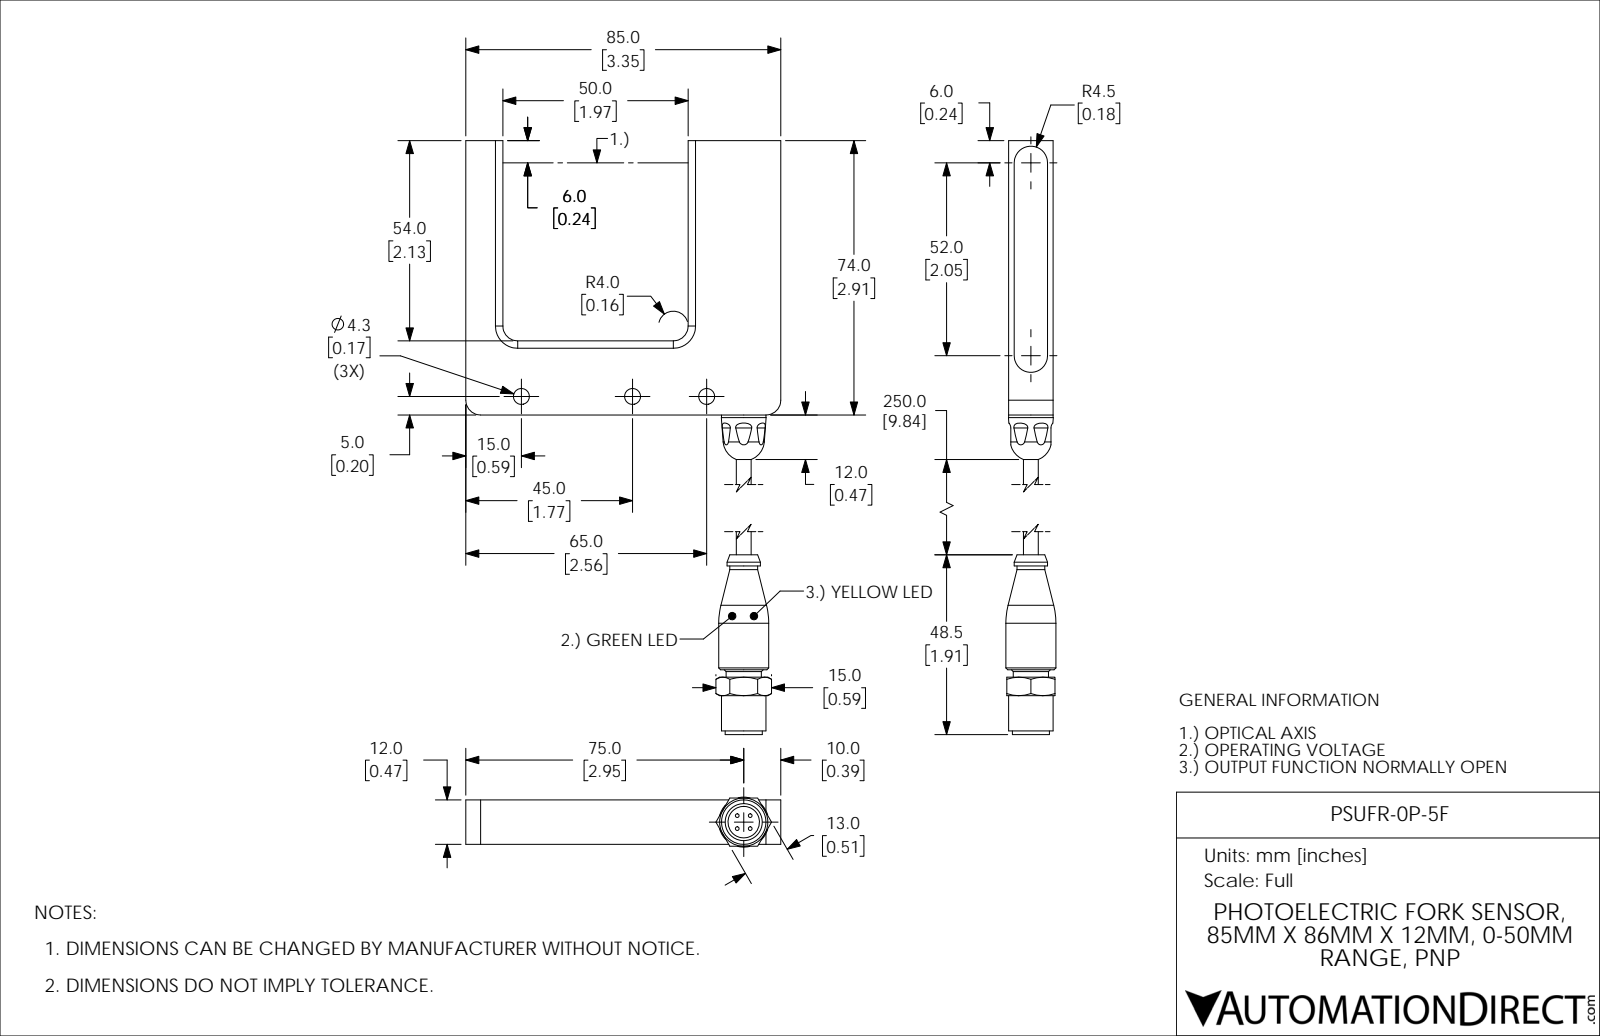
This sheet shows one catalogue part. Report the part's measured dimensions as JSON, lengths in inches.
{"part_name": "PSUFR-0P-5F", "step_written_by": "SolidWorks 2017 (AUTOMOTIVE_DESIGN)", "units": "inches", "bodies": {"solids": 2, "faces": 109, "planar": 43, "cylindrical": 39, "other": 27}, "overall_size": [8.445, 3.346, 0.531], "volume_in3": 2.969, "surface_area_in2": 24.36, "round_holes": [[0.169, 3], [0.173, 1], [0.335, 1]], "round_bosses_or_shafts": [[0.039, 4], [0.531, 1], [0.472, 1], [0.394, 1], [0.374, 1], [0.354, 1], [0.295, 1], [0.157, 1]], "partial_cylinders_radius": [[0.079, 12], [0.157, 4], [0.177, 2]], "face_to_face_distances": [0.472, 3.343, 3.339, 2.913, 0.98, 0.39, 2.358, 1.969, 2.949, 0.787], "hole_center_spacings": [0.787, 1.181, 1.969]}
